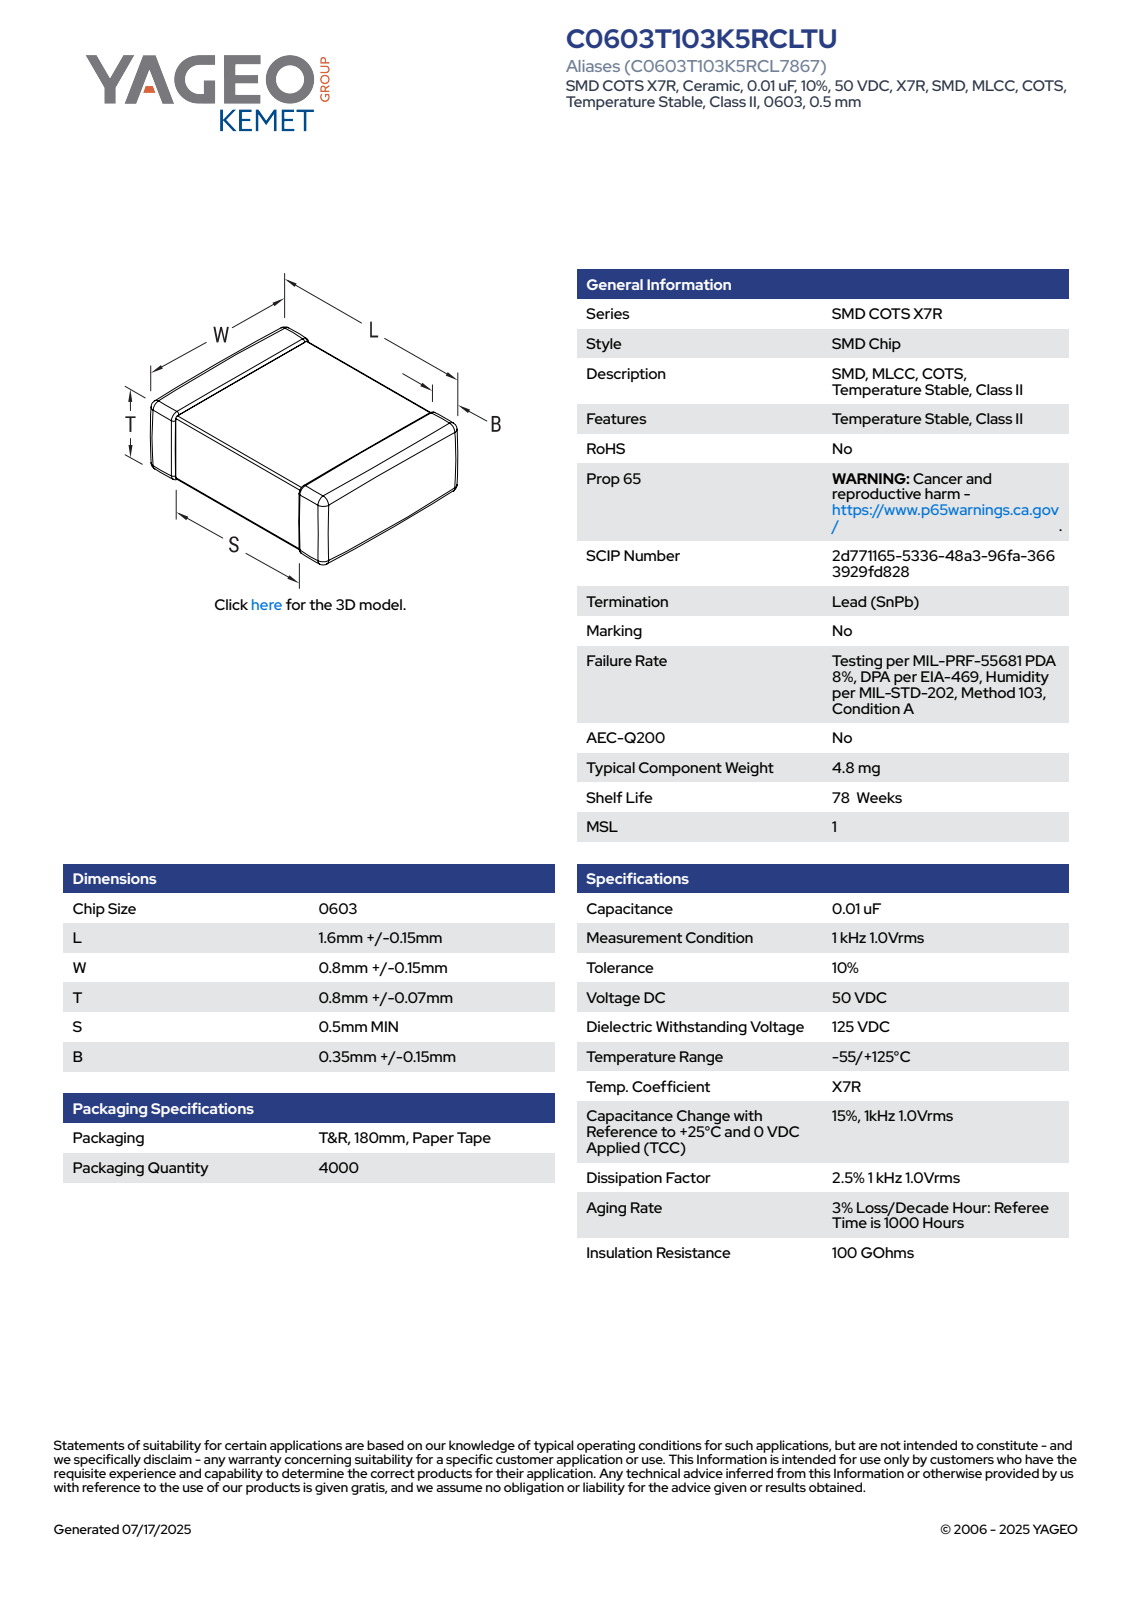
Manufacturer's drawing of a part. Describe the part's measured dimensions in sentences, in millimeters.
The part is named "CCSM_STD_0603_L1.75W0.95T0.87S0.8B0.5". Its 3-D file was written by "SolidWorks 2021 (AUTOMOTIVE_DESIGN)". It is 4 solids with 121 faces: 71 planar, 34 cylindrical and 16 other. Overall it measures 1.75 by 0.95 by 0.87 millimeters. Its volume is 1 cubic millimeters and its surface area 8 square millimeters. The main face-to-face distances are 0.85, 0.93, 0.87, 0.95, 1.75, 0.83, 0.91, 0.86, 0.84, 0.81.
